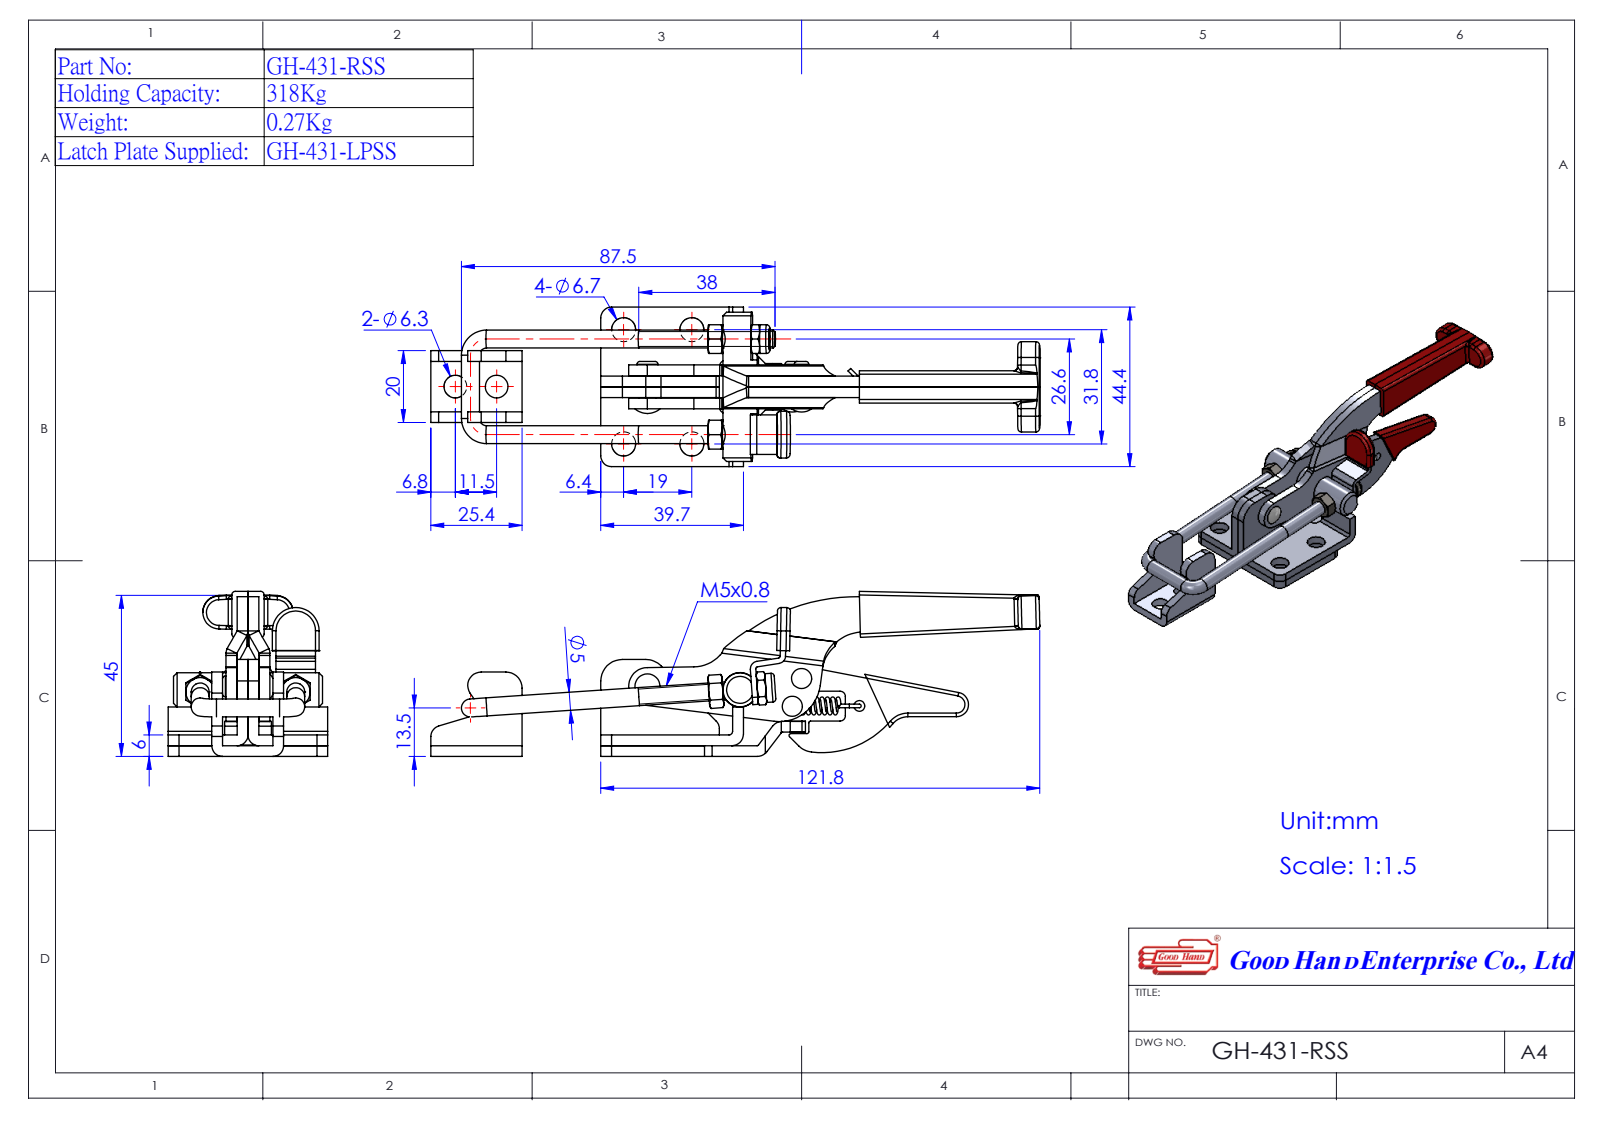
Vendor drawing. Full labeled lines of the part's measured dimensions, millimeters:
Part name (STEP PRODUCT): GH-431-LP-1^GH-431-R(簡化); GH-431-RSS(簡化); Group2^GH-431-R(簡化); Group3^GH-431-R(簡化) (+2 more)
STEP written by: SolidWorks 2016 (AUTOMOTIVE_DESIGN)
Units: millimetres
Bodies: 7 solids, 450 faces (177 planar, 174 cylindrical, 99 other)
Overall size (bounding box): 169.56 × 45.96 × 44.4
Volume: 39 933 mm³ · Surface area: 26 233 mm²
Round holes (diameter × count): ⌀4.2 ×4, ⌀5 ×4, ⌀6.7 ×4, ⌀5.3 ×2, ⌀5.86 ×2, ⌀6.3 ×2, ⌀4 ×1, ⌀5.1 ×1, ⌀9.5 ×1
Round bosses / shafts (diameter × count): ⌀5 ×3, ⌀8 ×2, ⌀5.8 ×1, ⌀4 ×1, ⌀3 ×1
Partial cylindrical surfaces — rounded edges, fillets, slot ends (radius × count): R0.5 ×7, R3 ×7, R11.5 ×5, R1 ×4, R2 ×4, R3.01 ×4, R52.32 ×4, R3.5 ×3
Main face-to-face distances: 3, 6, 1.5, 7.62, 1.62, 4.62, 6.12, 3.12, 9.12, 9.24
Hole centre spacings: 26.6, 19, 31.8, 37.04, 11.5, 25.8, 38.73, 38.79
